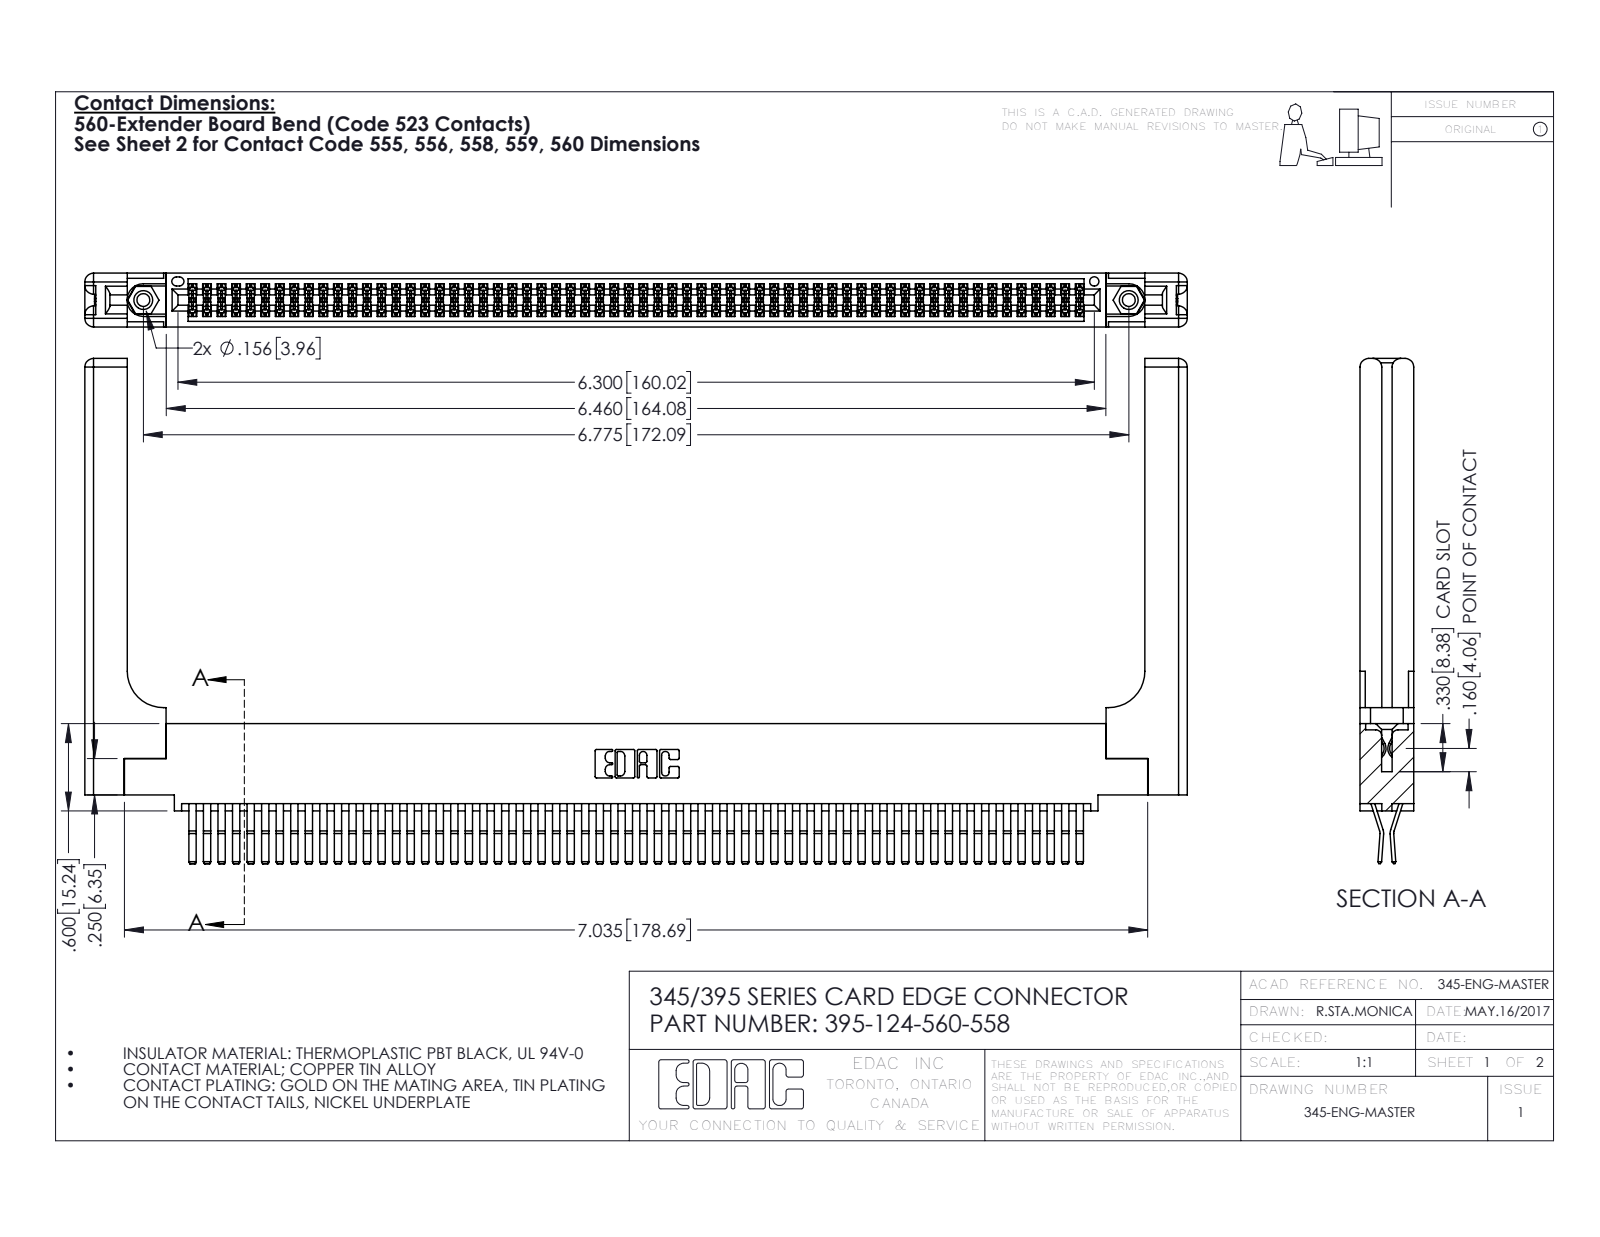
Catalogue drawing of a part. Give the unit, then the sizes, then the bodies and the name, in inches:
Units: inches
Overall size (bounding box): 7.579 × 3.472 × 0.37
Round holes (diameter × count): ⌀0.089 ×2, ⌀0.125 ×2, ⌀0.156 ×2, ⌀0.064 ×1
Round bosses / shafts (diameter × count): ⌀0.155 ×2
Partial cylindrical surfaces — rounded edges, fillets, slot ends (radius × count): R0.006 ×187, R0.01 ×22, R0.06 ×16, R0.007 ×6, R0.031 ×6, R0.026 ×3, R0.01 ×2, R0.014 ×2
Main face-to-face distances: 0.072, 0.298, 0.025, 0.37, 0.098, 0.272, 0.2, 0.225, 0.15, 0.148
Hole centre spacings: 0.27, 6.539, 6.775
Volume: 1.715 in³ · Surface area: 56.79 in²
Bodies: 129 solids, 6834 faces (4324 planar, 2450 cylindrical, 60 other)
Part name (STEP PRODUCT): 345-220-058_345-220-058; 345 Part_0.110 Offset - 0.156 Dia-TH; 395-124-560-558; 345-292-001_560 Tail (+1 more)
STEP written by: SolidWorks 2016 (CONFIG_CONTROL_DESIGN)
